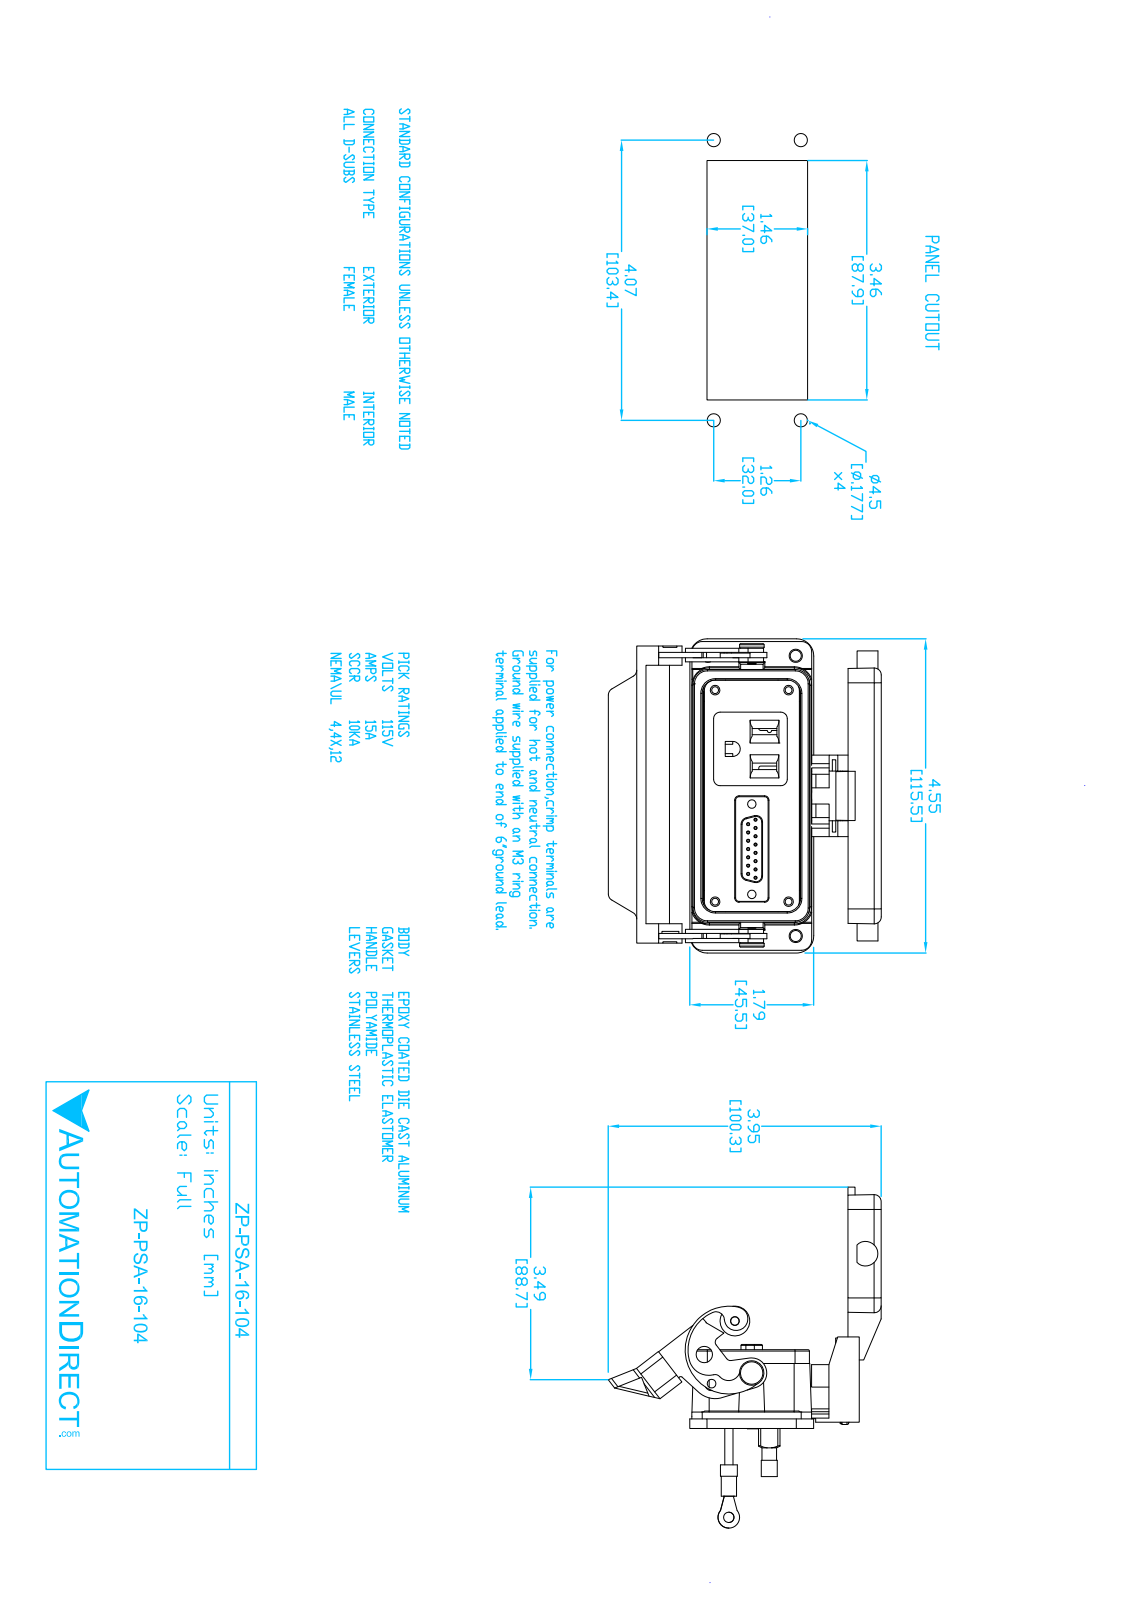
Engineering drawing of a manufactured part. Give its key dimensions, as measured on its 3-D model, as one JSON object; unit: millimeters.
{"part_name": "ZP-PSA-16-104", "step_written_by": "SolidWorks 2017 (AUTOMOTIVE_DESIGN)", "units": "millimeters", "bodies": {"solids": 1, "faces": 1626, "planar": 884, "cylindrical": 478, "other": 264}, "overall_size": [125.3, 115.5, 100.8], "volume_mm3": 100500, "surface_area_mm2": 68130, "round_holes": [[1.1, 15], [4.1, 6], [2.5, 4], [3.7, 4], [4.8, 4], [2.3, 2], [3, 2], [3.1, 2], [3.4, 2], [3.8, 2], [5.1, 2], [1.9, 1]], "round_bosses_or_shafts": [[1, 15], [5.6, 4], [3, 4], [5.8, 2], [5.3, 2], [2.8, 2], [2.5, 2], [10.9, 1]], "partial_cylinders_radius": [[2.5, 16], [3.8, 13], [0.8, 12], [0.5, 10], [0.4, 9], [0.3, 8], [0.6, 8], [2.4, 8]], "face_to_face_distances": [1.2, 17.1, 18.3, 3.4, 2.9, 40.7, 0.5, 9.3, 39.2, 1.5], "hole_center_spacings": [3, 6.1, 3.2, 5.4, 12.2, 15.2, 8, 9.1]}
